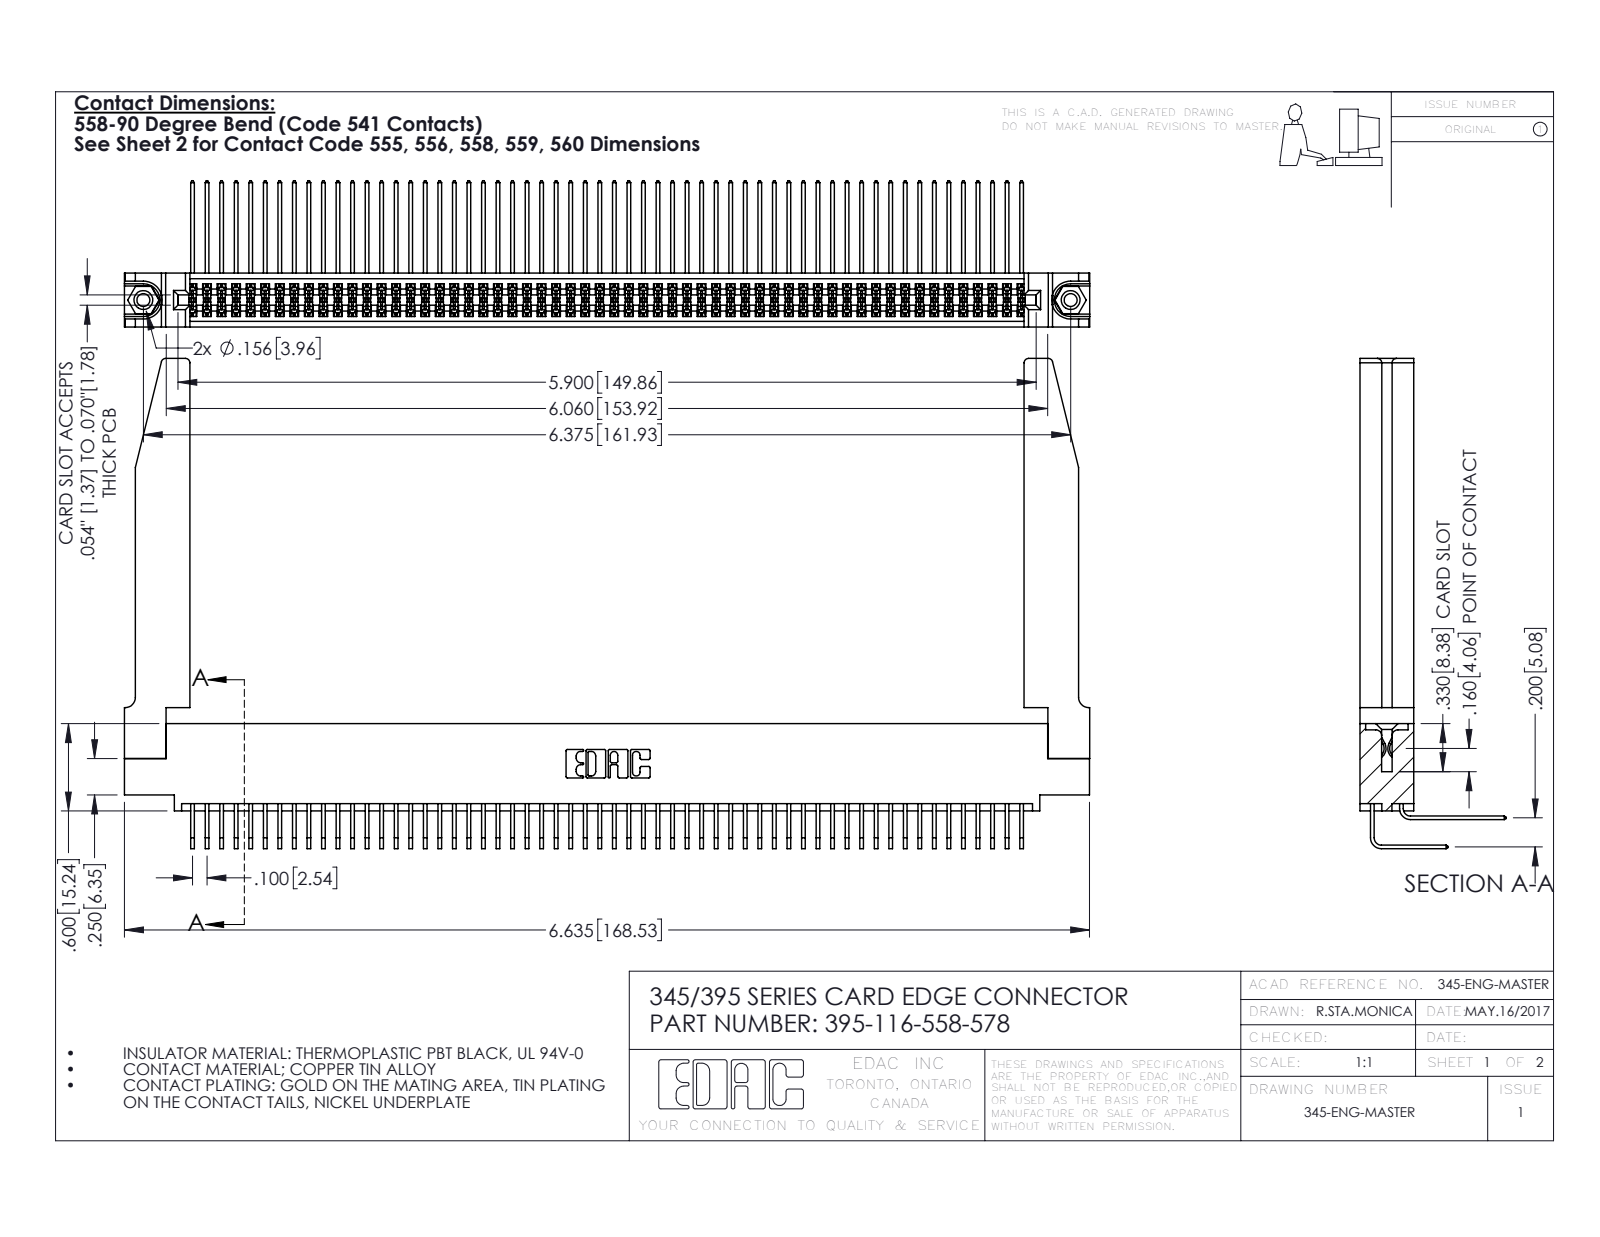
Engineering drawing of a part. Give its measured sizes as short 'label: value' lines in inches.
name: 345 Part_0.110 Offset - 0.156 Dia-TH; 395-116-558-578; 345-292-001_558 559 Tail - 1; 345-292-001_558 Tail - 2 (+2 more)
written by: SolidWorks 2016 (CONFIG_CONTROL_DESIGN)
unit: in
bodies: 121 solids, 6396 faces (4286 planar, 2058 cylindrical, 52 other)
size: 6.636 × 3.369 × 1.005
volume: 1.519 in³; area: 55.32 in²
holes: 2× ⌀0.089, 2× ⌀0.125, 2× ⌀0.156, 1× ⌀0.064
bosses: 2× ⌀0.155
rounds: 174× R0.006, 22× R0.01, 8× R0.03, 6× R0.007, 6× R0.031, 3× R0.026, 2× R0.014, 2× R0.019
face distances: 0.072, 0.298, 0.37, 0.2, 0.098, 0.272, 0.025, 0.225, 0.025, 0.175
hole spacings: 0.27, 6.139, 6.375
